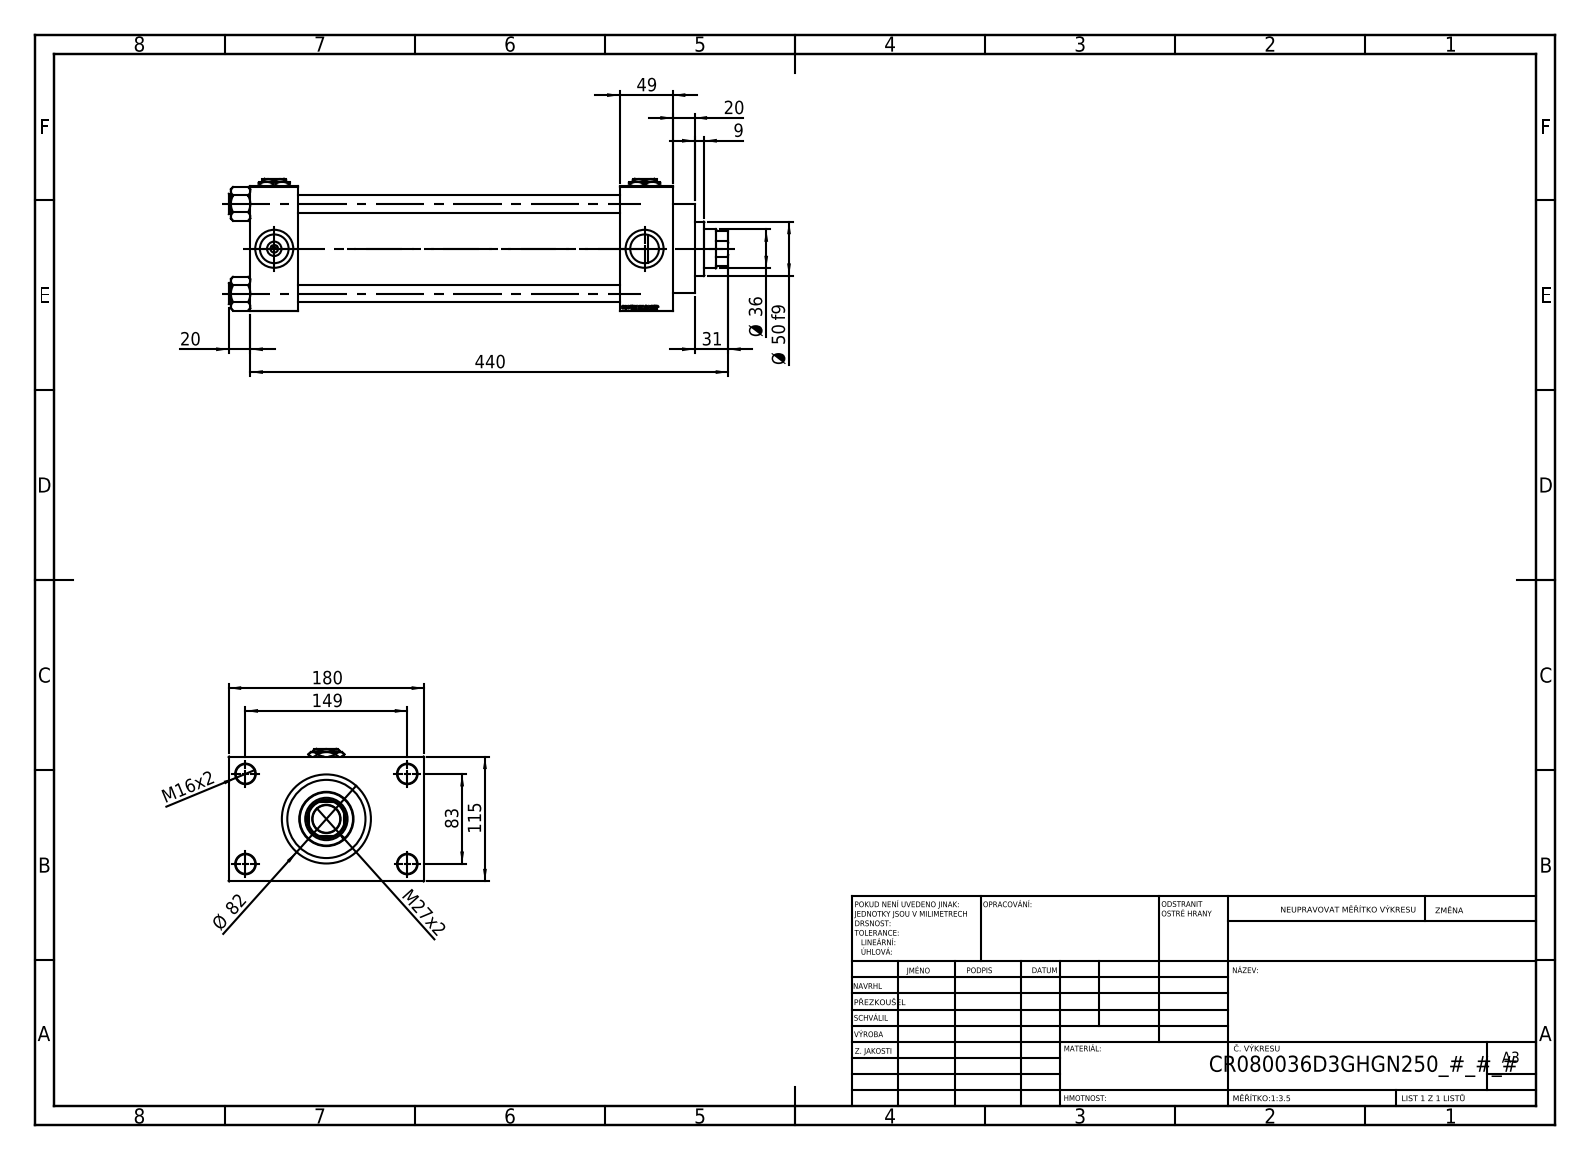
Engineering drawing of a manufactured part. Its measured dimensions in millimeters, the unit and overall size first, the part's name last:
Units: millimetres
Overall size (bounding box): 460 × 180 × 122
Round holes (diameter × count): ⌀16 ×4, ⌀18 ×4, ⌀26.44 ×4, ⌀35 ×4, ⌀7 ×3, ⌀25.5 ×1, ⌀36 ×1, ⌀39 ×1, ⌀61 ×1, ⌀72 ×1, ⌀80 ×1
Round bosses / shafts (diameter × count): ⌀19 ×4, ⌀86 ×1, ⌀82 ×1, ⌀50 ×1
Partial cylindrical surfaces — rounded edges, fillets, slot ends (radius × count): R17.5 ×1
Main face-to-face distances: 115, 296, 345, 49, 44, 340, 389, 32.5, 147.5, 180
Hole centre spacings: 33.15, 58.48, 82.7, 85.28, 89.24, 115.85, 142.43, 83
Volume: 2 565 000 mm³ · Surface area: 495 508 mm²
Bodies: 13 solids, 1252 faces (593 planar, 99 cylindrical, 560 other)
Part name (STEP PRODUCT): V215_VC_A; V215CR_D_TYCINKA; V215CR_VCP_D; Zatka_pro_OIL_PORT (+2 more)
STEP written by: SolidWorks 2019 (CONFIG_CONTROL_DESIGN)
